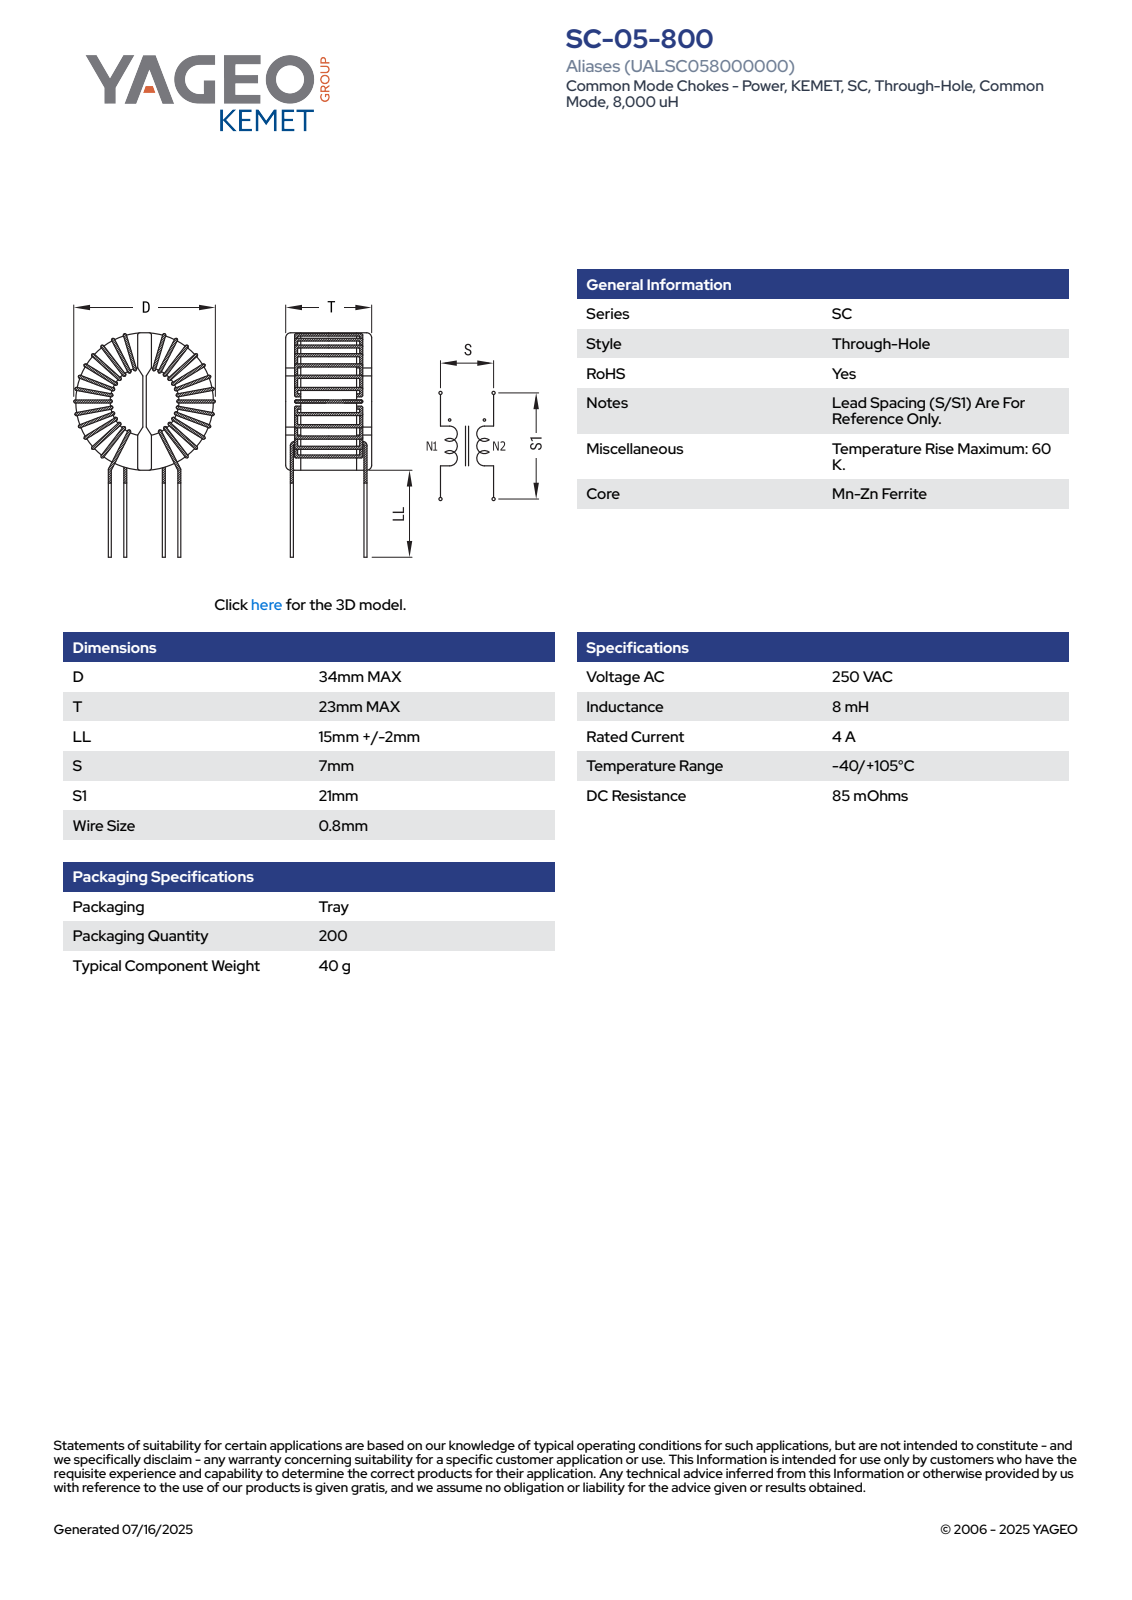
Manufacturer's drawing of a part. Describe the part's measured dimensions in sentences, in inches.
The part is named "SC-05-800". Its 3-D file was written by "SolidWorks 2018 (AUTOMOTIVE_DESIGN)". It is 1 solid with 269 faces: 113 planar, 85 cylindrical and 71 other. Overall it measures 1.784 by 1.339 by 0.906 inches. Its volume is 0.922 cubic inches and its surface area 10.05 square inches. Round bosses or shafts: 8 of diameter 0.031. Partial cylindrical surfaces (rounded edges, fillets, slot ends): 16 of radius 0.016, 6 of radius 0.008, 2 of radius 0.02, 1 of radius 0.177, 1 of radius 0.262, 1 of radius 0.289, 1 of radius 0.293, 1 of radius 0.295. The main face-to-face distances are 0.795, 0.047, 0.079, 0.031, 0.126, 0.098, 0.697, 0.055, 0.85, 0.752.
